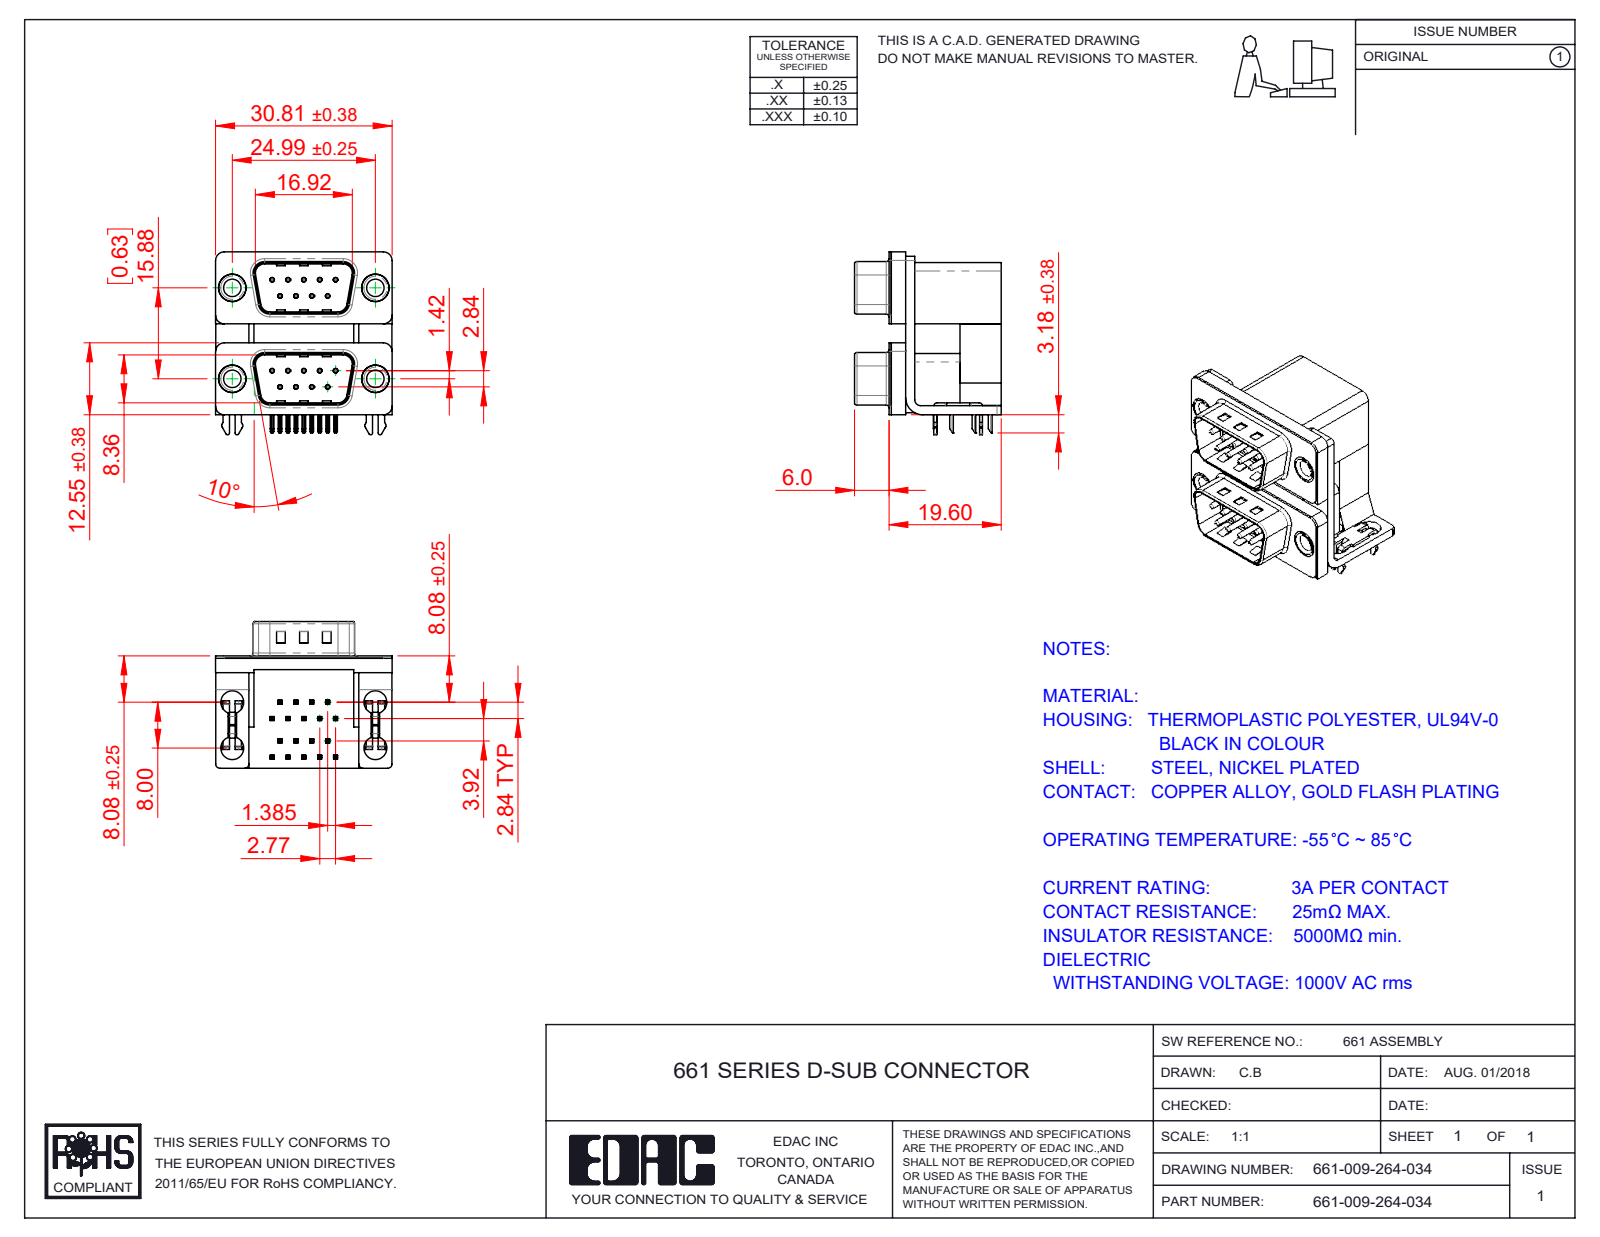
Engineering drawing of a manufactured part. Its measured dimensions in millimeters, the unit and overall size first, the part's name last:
Units: millimetres
Overall size (bounding box): 31.93 × 30.81 × 25.6
Round holes (diameter × count): ⌀0.35 ×18, ⌀0.8 ×18, ⌀4 ×8, ⌀3.05 ×4, ⌀3.5 ×4, ⌀4.8 ×4, ⌀5 ×4
Round bosses / shafts (diameter × count): ⌀0.75 ×18, ⌀4.9 ×4, ⌀4.75 ×4, ⌀3.85 ×4
Partial cylindrical surfaces — rounded edges, fillets, slot ends (radius × count): R0.25 ×82, R0.12 ×36, R0.5 ×20, R1.5 ×13, R0.75 ×10, R0.9 ×8, R1.6 ×8, R2 ×8
Main face-to-face distances: 0.4, 2.5, 16.7, 19.2, 9.5, 15.87, 7.2, 12, 1.6, 19.6
Hole centre spacings: 3.16, 16.12, 2.77, 15.88, 16.82, 18.77, 5.54, 5.04
Volume: 9 817 mm³ · Surface area: 11 603 mm²
Bodies: 31 solids, 2016 faces (1254 planar, 608 cylindrical, 154 other)
Part name (STEP PRODUCT): 661 Contact Bottom Lower; 661 Shell_09 Contacts; 661 Housing Spacer_09 Contacts L; 661 2 Prong Board Lock_3 (+8 more)
STEP written by: SolidWorks 2020 (CONFIG_CONTROL_DESIGN)
